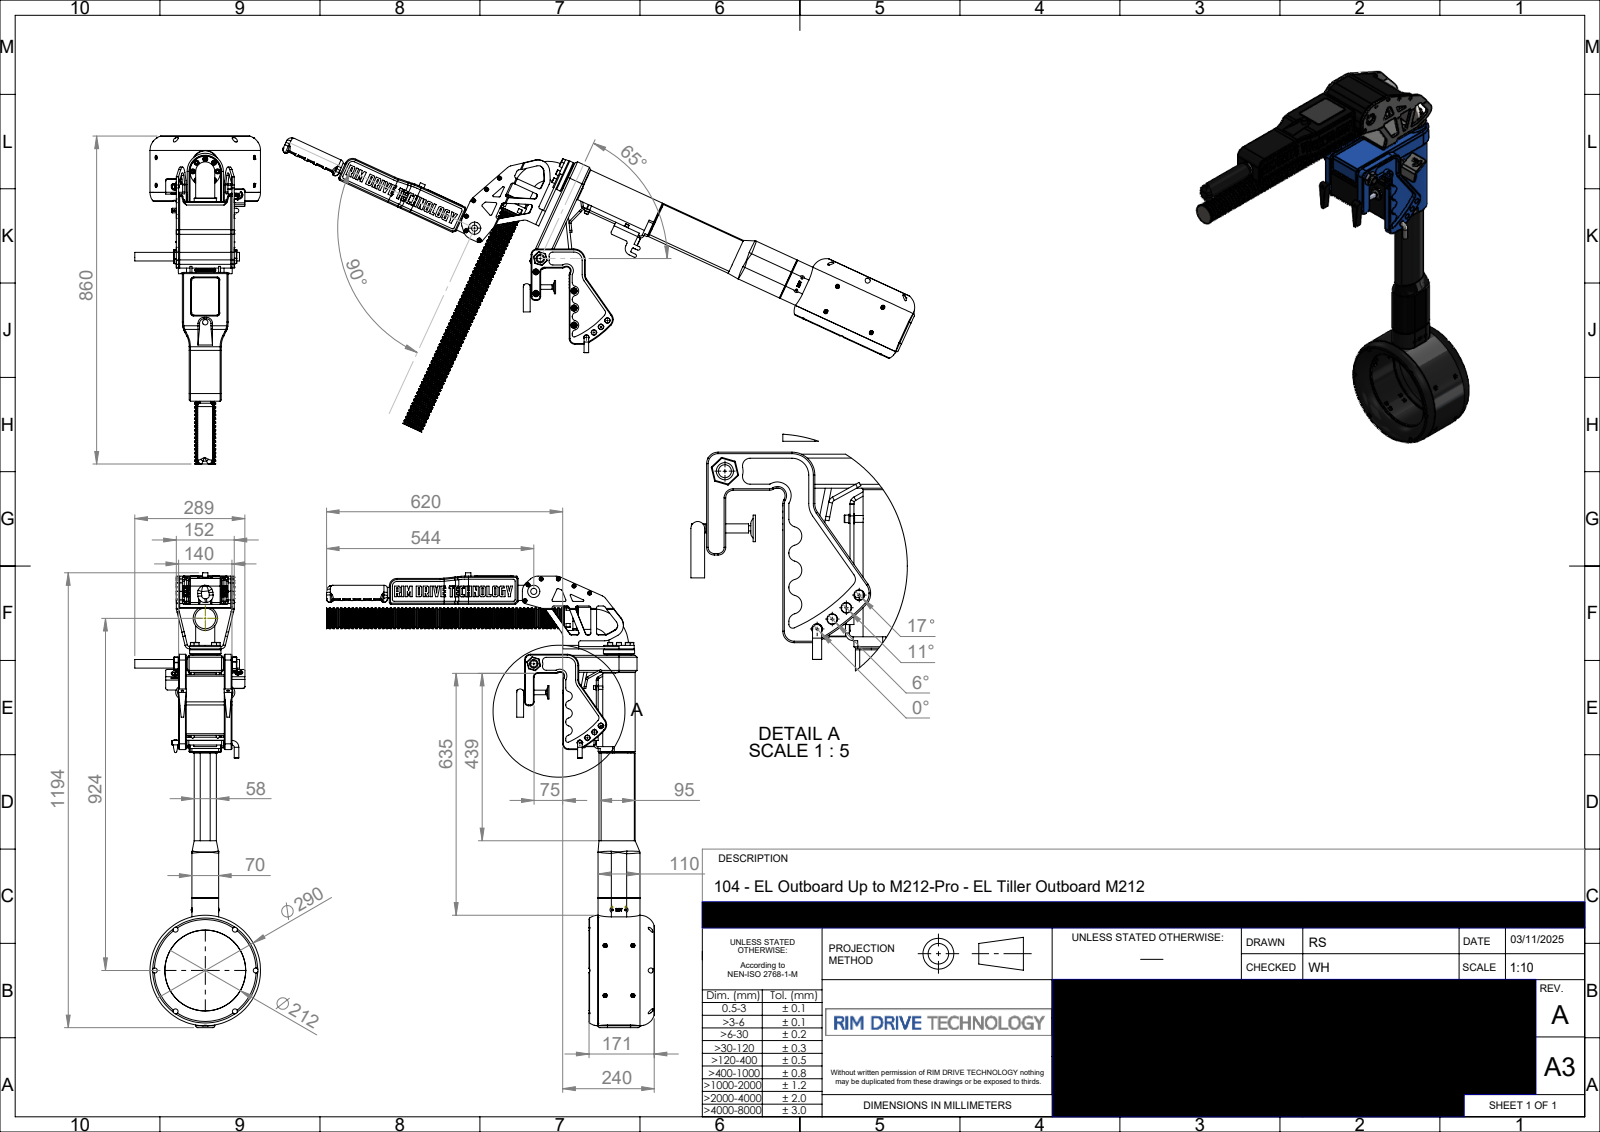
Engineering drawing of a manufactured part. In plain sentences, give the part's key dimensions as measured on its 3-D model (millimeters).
The part is named "P-104-250-rev-A-212". Its 3-D file was written by "SolidWorks 2024 (AUTOMOTIVE_DESIGN)". It is 1 solid with 4873 faces: 2351 planar, 805 cylindrical and 1717 other. Overall it measures 1193.7 by 860.41 by 330 millimeters. Its volume is 16 080 000 cubic millimeters and its surface area 1 512 000 square millimeters. Round holes: 6 of diameter 4.2, 5 of diameter 5, 4 of diameter 13, 2 of diameter 3.5, 2 of diameter 5.3, 1 of diameter 4, 1 of diameter 17, 1 of diameter 32, 1 of diameter 85, 1 of diameter 212, 1 of diameter 220. Round bosses or shafts: 37 of diameter 9.64, 27 of diameter 5, 8 of diameter 13, 7 of diameter 12, 4 of diameter 10, 3 of diameter 8.1, 2 of diameter 35, 2 of diameter 6.95. Partial cylindrical surfaces (rounded edges, fillets, slot ends): 60 of radius 3, 50 of radius 5, 43 of radius 0.5, 34 of radius 10, 26 of radius 2, 25 of radius 1, 12 of radius 6, 7 of radius 15. The main face-to-face distances are 6, 20, 10, 5, 120, 15, 110, 100, 12.5, 95. The hole center spacings are 73, 239.77, 23.7, 36.5, 47.35, 61.28, 732.16, 23.71.
